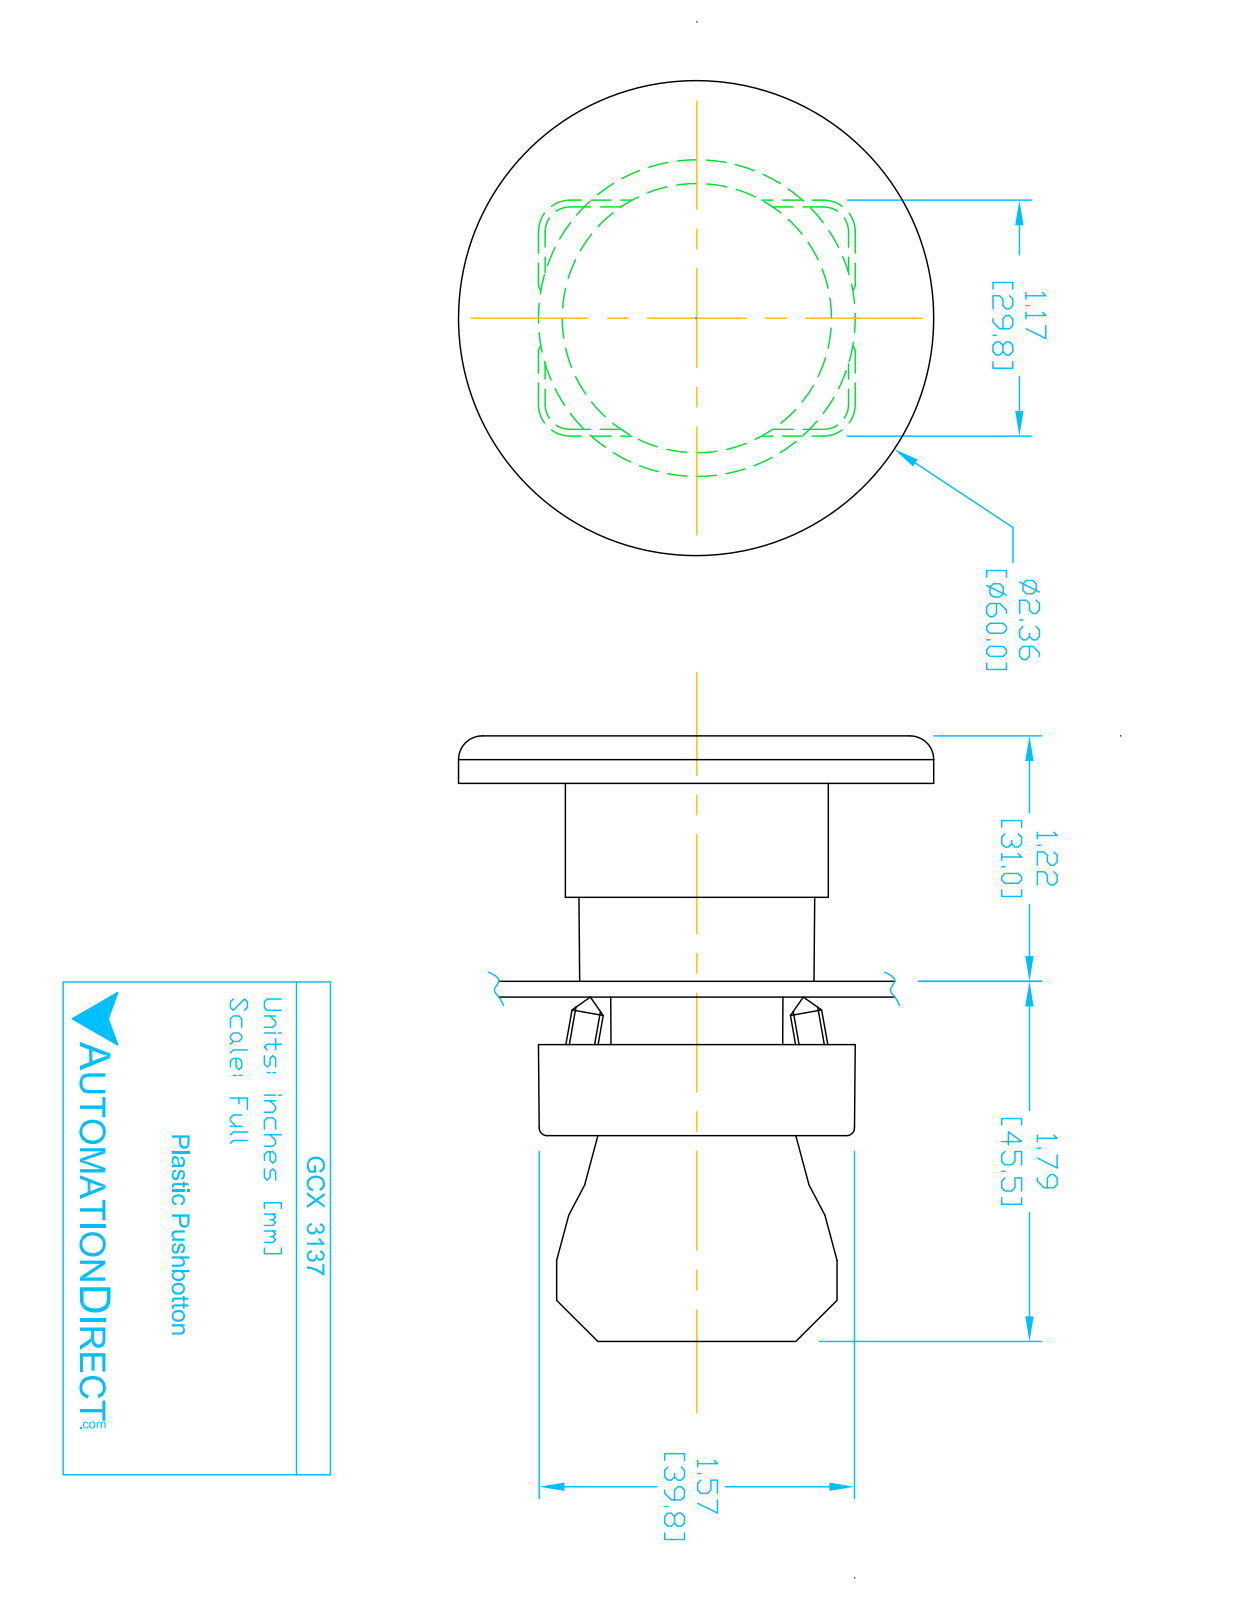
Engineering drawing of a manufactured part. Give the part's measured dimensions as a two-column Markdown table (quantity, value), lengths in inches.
| quantity | value |
| --- | --- |
| part name | GCX3137; ecx1030; GCX3137 OPERATOR; ECX3029-2 |
| STEP written by | SolidWorks 2016 (AUTOMOTIVE_DESIGN) |
| units | inches |
| bodies | 6 solids, 391 faces (224 planar, 136 cylindrical, 31 other) |
| overall size | 2.944 × 2.362 × 2.362 |
| volume | 2.416 in³ |
| surface area | 38.68 in² |
| round holes (diameter × count) | 0.079 × 2, 0.124 × 2, 0.13 × 2, 0.087 × 1, 0.197 × 1, 0.878 × 1, 0.888 × 1, 1.024 × 1, 1.181 × 1 |
| round bosses / shafts (diameter × count) | 0.157 × 2, 2.362 × 1, 1.299 × 1, 1.175 × 1, 0.945 × 1, 0.856 × 1, 0.78 × 1 |
| partial cylindrical surfaces (radius × count) | 0.059 × 24, 0.041 × 12, 0.124 × 12, 0.157 × 12, 0.039 × 4, 0.128 × 2, 0.02 × 1, 0.063 × 1 |
| main face-to-face distances | 0.236, 1.685, 1.921, 0.579, 0.033, 1.763, 0.079, 0.157, 0.031, 0.72 |
| hole center spacings | 0.236, 0.544, 0.472, 0.49 |
